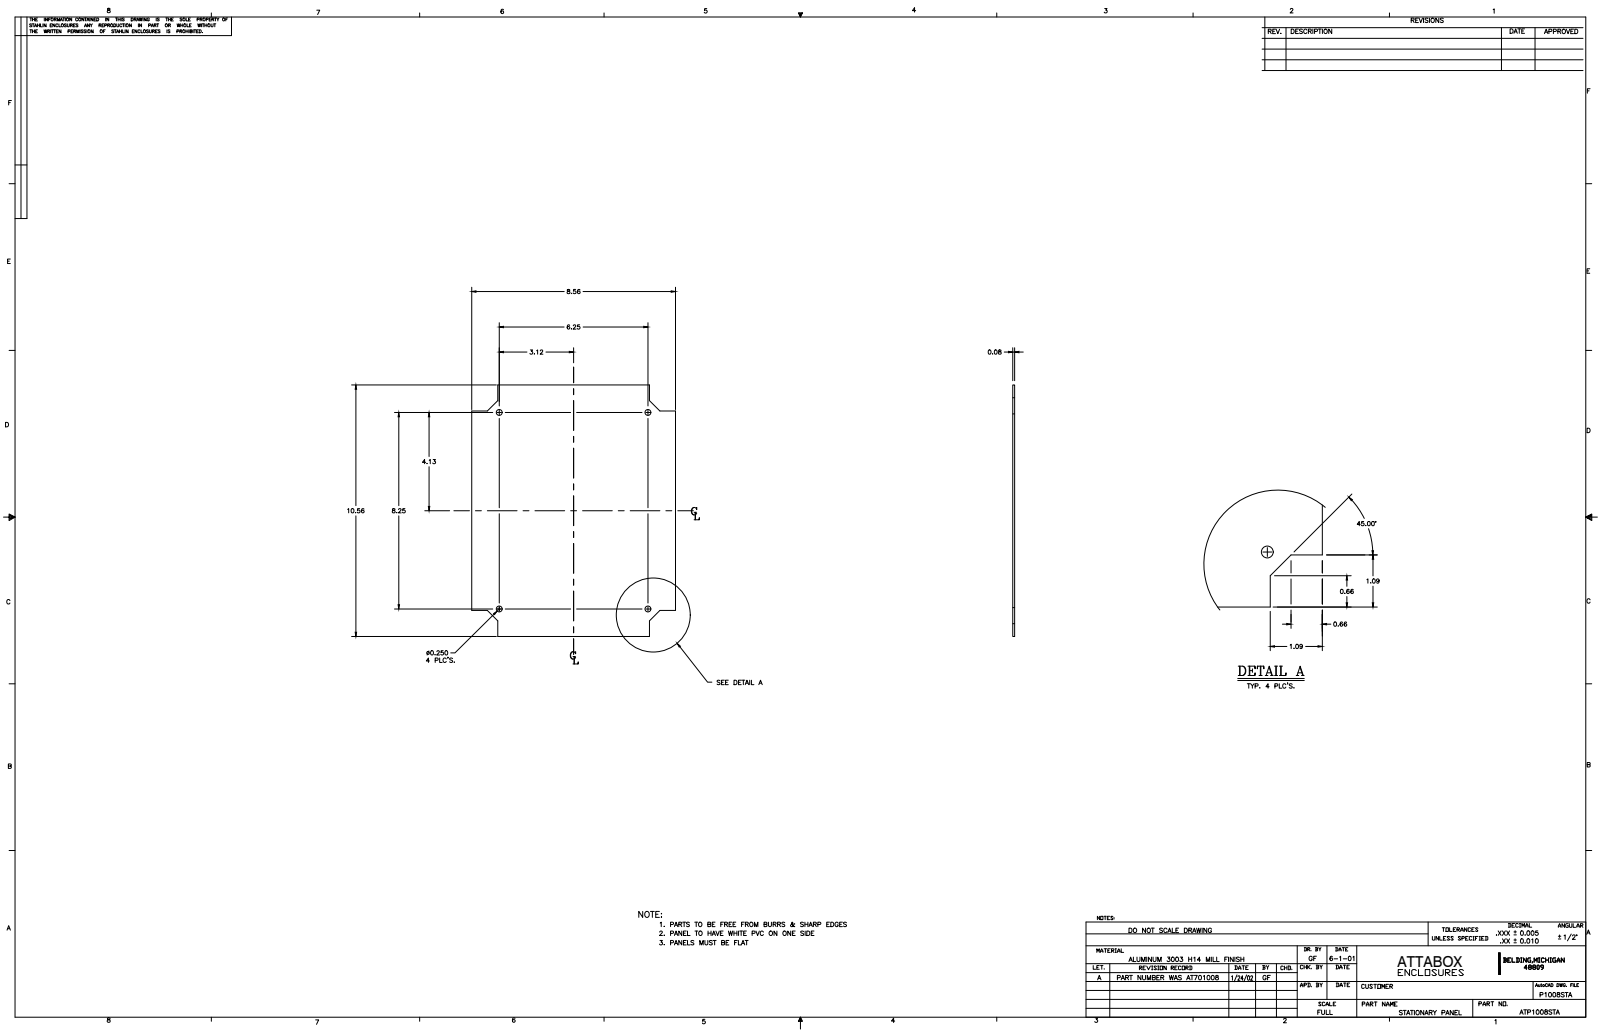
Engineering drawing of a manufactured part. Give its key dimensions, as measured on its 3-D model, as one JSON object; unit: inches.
{"part_name": "P1008STAL", "step_written_by": "Autodesk Inventor 11 (AUTOMOTIVE_DESIGN)", "units": "inches", "bodies": {"solids": 1, "faces": 22, "planar": 18, "cylindrical": 4, "other": 0}, "overall_size": [10.563, 8.563, 0.08], "volume_in3": 6.867, "surface_area_in2": 174.9, "round_holes": [[0.25, 4]], "face_to_face_distances": [0.08, 8.562, 10.562, 1.094, 7.468, 9.468, 6.374, 8.374, 11.045], "hole_center_spacings": [6.25, 8.25, 10.35, 10.35]}
